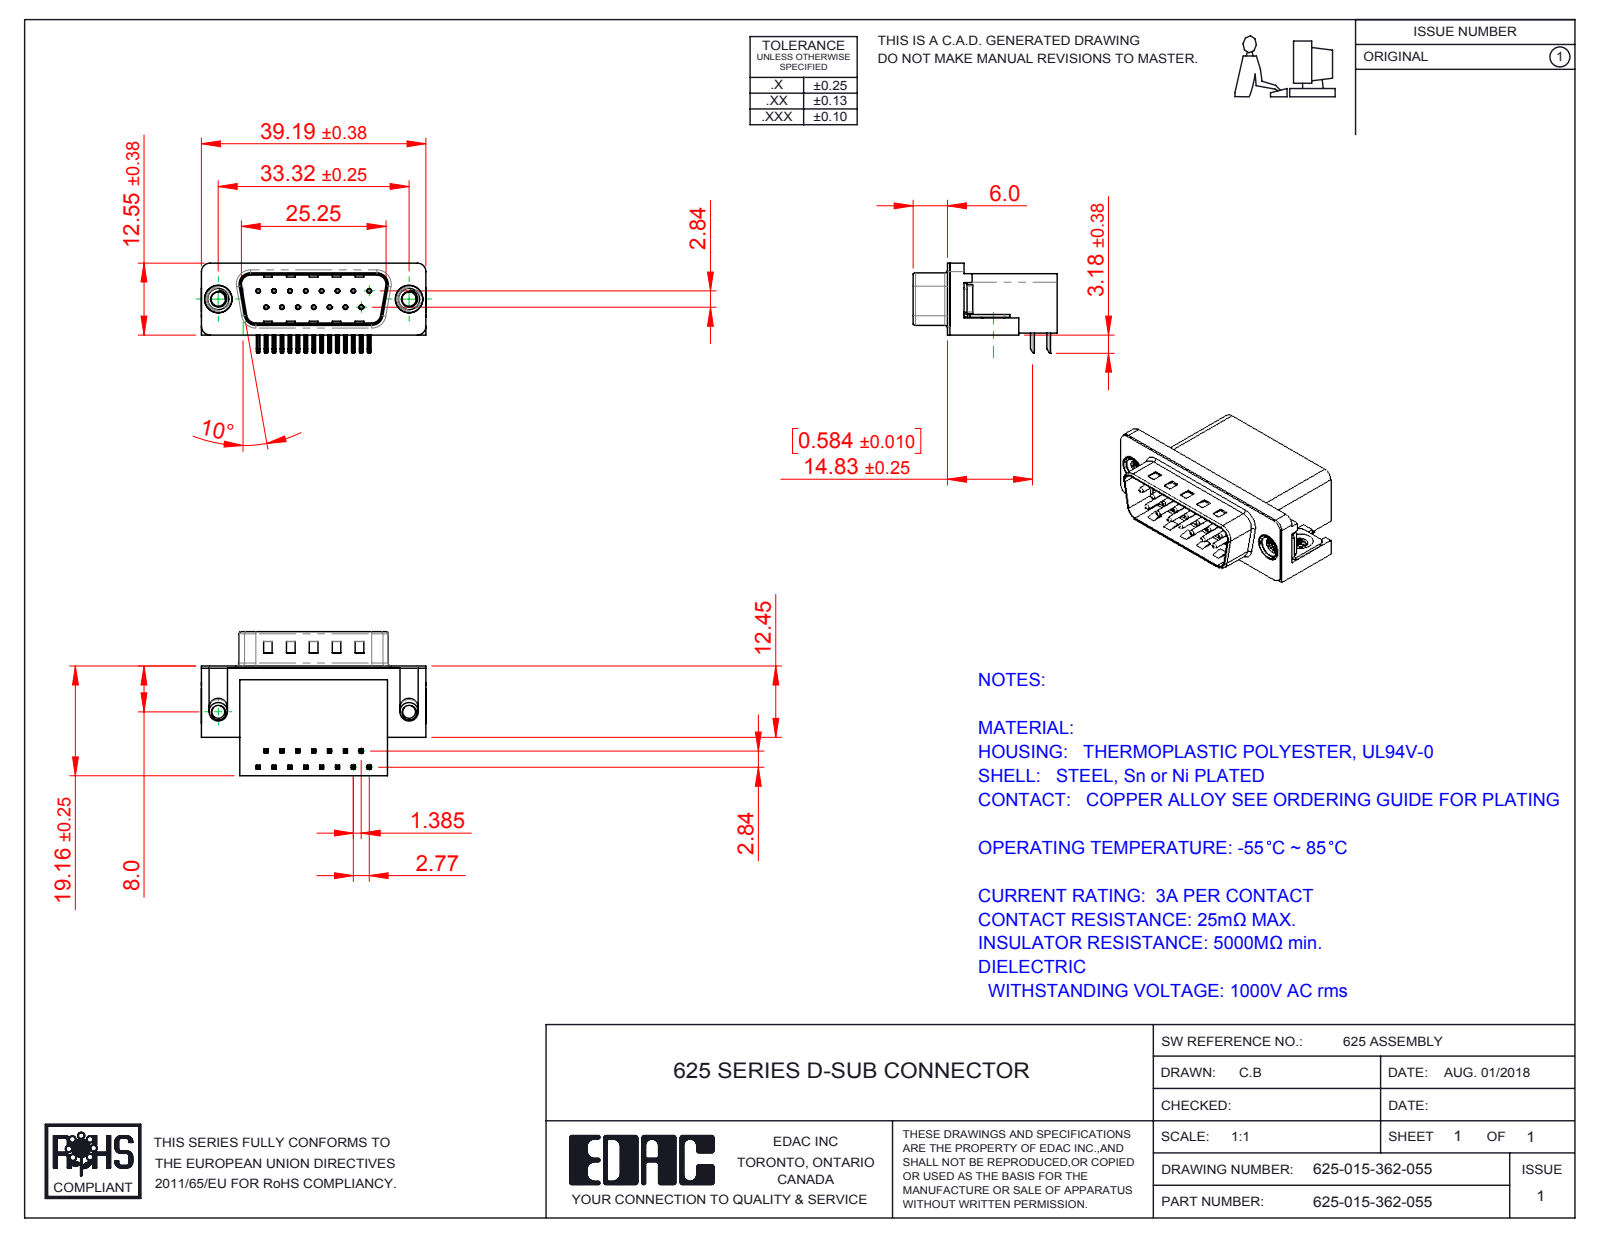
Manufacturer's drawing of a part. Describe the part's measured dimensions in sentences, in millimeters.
The part is named "625 4-40 Threaded Board Mount; 625 Contact Bottom; 625 Housing_15 Socket; 625 Shell_15 Socket (+3 more)". Its 3-D file was written by "SolidWorks 2016 (CONFIG_CONTROL_DESIGN)". It is 21 solids with 1511 faces: 895 planar, 463 cylindrical and 153 other. Overall it measures 39.22 by 25.16 by 15.73 millimeters. Its volume is 6 248 cubic millimeters and its surface area 6 507 square millimeters. Round holes: 15 of diameter 0.35, 15 of diameter 0.8, 2 of diameter 2.26, 2 of diameter 2.5, 2 of diameter 4, 2 of diameter 4.8, 2 of diameter 5. Round bosses or shafts: 15 of diameter 0.75, 2 of diameter 4.9, 2 of diameter 4.75, 2 of diameter 3.9, 2 of diameter 3.26. Partial cylindrical surfaces (rounded edges, fillets, slot ends): 68 of radius 0.25, 30 of radius 0.12, 16 of radius 1, 9 of radius 0.5, 8 of radius 1.6, 6 of radius 1.5, 4 of radius 0.9, 4 of radius 2. The main face-to-face distances are 0.4, 10.35, 18.76, 2.1, 10.46, 19.16, 1.7, 10.86, 8.76, 16.26. The hole center spacings are 3.16, 2.77, 5.54, 8.31, 11.08, 5.03, 5.04, 7.48.
